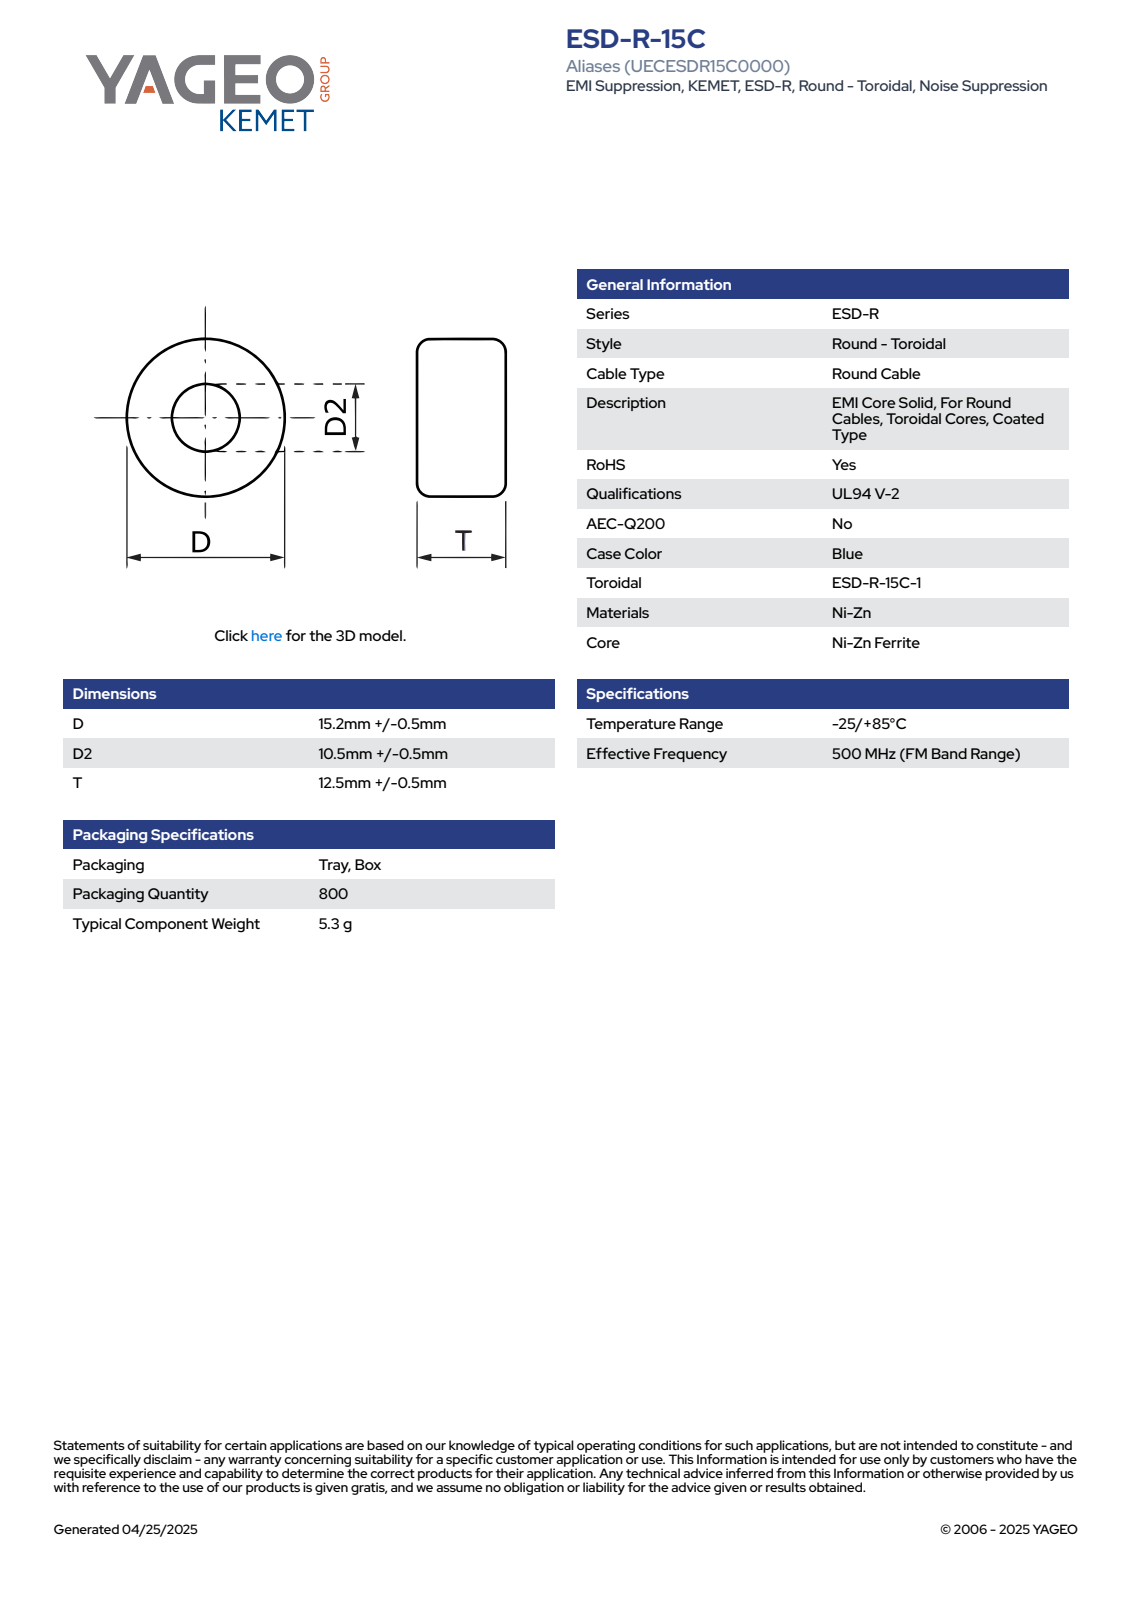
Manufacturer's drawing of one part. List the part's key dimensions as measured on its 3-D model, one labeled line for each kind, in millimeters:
Part name (STEP PRODUCT): EC_KBC_D15.7D210.5T13
STEP written by: SolidWorks 2021 (AUTOMOTIVE_DESIGN)
Units: millimetres
Bodies: 1 solid, 66 faces (24 planar, 7 cylindrical, 35 other)
Overall size (bounding box): 15.71 × 15.7 × 13
Volume: 1 386 mm³ · Surface area: 1 266 mm²
Round holes (diameter × count): ⌀10.5 ×1
Round bosses / shafts (diameter × count): ⌀15.7 ×1
Partial cylindrical surfaces — rounded edges, fillets, slot ends (radius × count): R7.86 ×1
Main face-to-face distances: 13, 5.65, 7.35, 1.7, 0.32, 5.97, 7.03, 1.38, 1.06, 6.71
